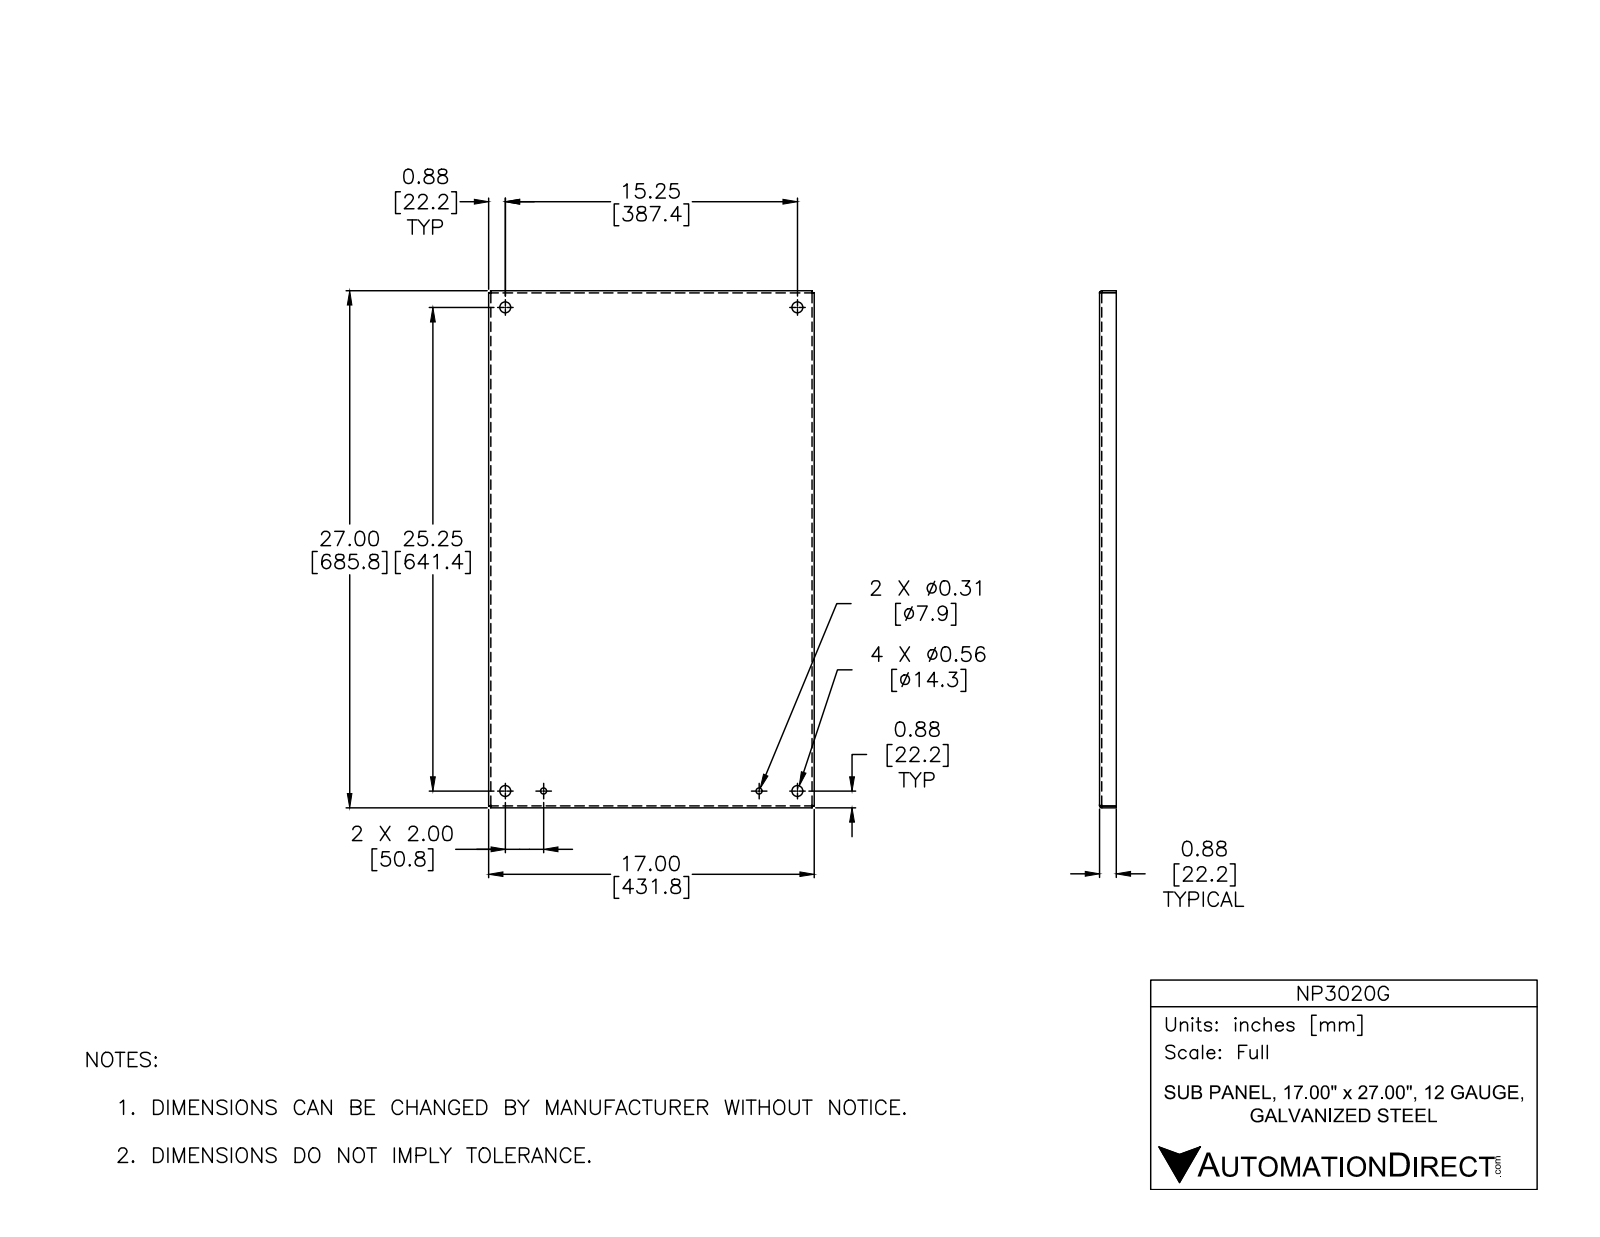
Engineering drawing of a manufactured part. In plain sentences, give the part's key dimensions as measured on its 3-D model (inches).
The part is named "NP3020G". Its 3-D file was written by "Autodesk Inventor 2012 (AUTOMOTIVE_DESIGN)". It is 1 solid with 44 faces: 22 planar, 14 cylindrical and 8 other. Overall it measures 27 by 17 by 0.875 inches. Its volume is 49 cubic inches and its surface area 1 056 square inches. Round holes: 4 of diameter 0.563, 2 of diameter 0.312. Partial cylindrical surfaces (rounded edges, fillets, slot ends): 4 of radius 0.031, 4 of radius 0.125. The main face-to-face distances are 0.094, 16.906, 26.906, 17, 16.813, 27, 26.813, 0.781, 0.875, 0.105. The hole center spacings are 2, 13.25, 15.25, 25.25, 25.329, 28.515, 29.498, 11.25.
